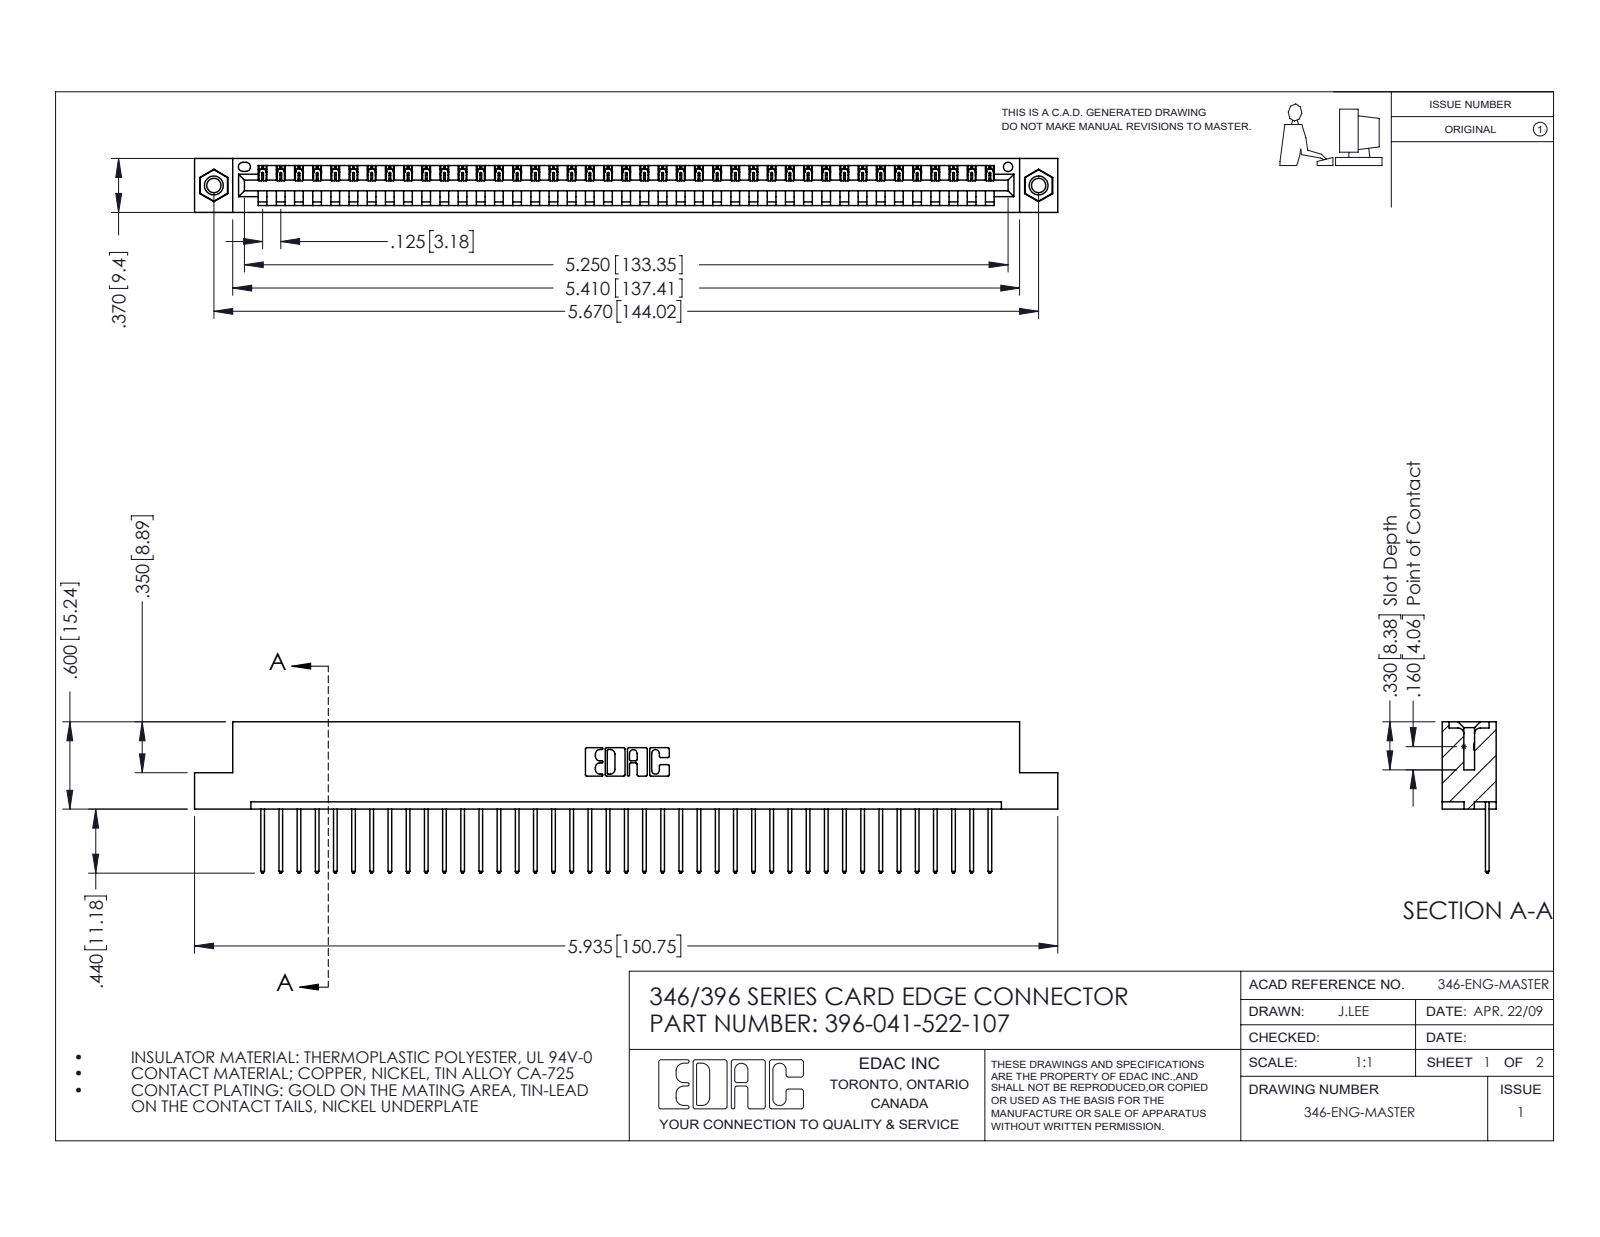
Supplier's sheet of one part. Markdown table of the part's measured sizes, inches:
| quantity | value |
| --- | --- |
| part name | 345-250-001_345-250-005-103; 396-041-522-107; 345-292-001_345-293-122; 346 Part_Flush Mounting Lugs - 0.156 Dia-TI |
| STEP written by | SolidWorks 2016 (CONFIG_CONTROL_DESIGN) |
| units | inches |
| bodies | 44 solids, 2560 faces (1748 planar, 796 cylindrical, 16 other) |
| overall size | 5.935 × 1.04 × 0.37 |
| volume | 0.88 in³ |
| surface area | 28.2 in² |
| round holes (diameter × count) | 0.098 × 2, 0.125 × 2, 0.156 × 2, 0.064 × 1 |
| round bosses / shafts (diameter × count) | 0.155 × 2 |
| partial cylindrical surfaces (radius × count) | 0.006 × 82, 0.01 × 82, 0.01 × 22, 0.007 × 6, 0.031 × 6, 0.026 × 3, 0.031 × 2, 0.04 × 2 |
| main face-to-face distances | 0.048, 0.322, 0.37, 0.25, 0.072, 0.298, 0.025, 0.148, 0.222, 0.1 |
| hole center spacings | 0.246, 5.461, 5.67 |
